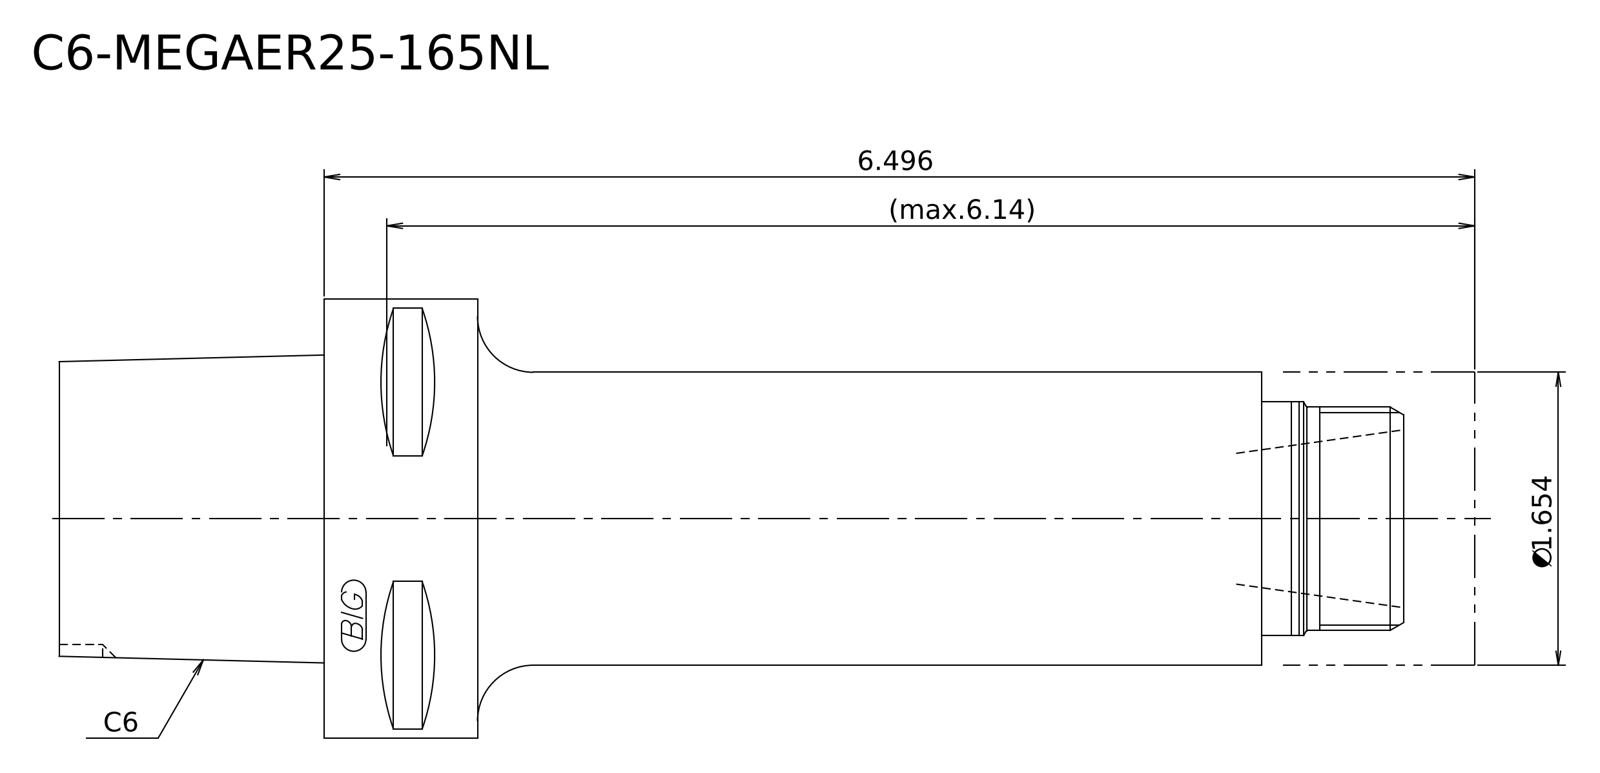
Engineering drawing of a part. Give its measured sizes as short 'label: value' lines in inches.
written by: Kubotek KeyCreator 2011 V10.0.2 (22737) (automotive_design)
unit: in
bodies: 2 solids, 18 faces (7 planar, 5 cylindrical, 6 other)
size: 7.992 × 2.48 × 2.48
volume: 20.67 in³; area: 59.33 in²
bosses: 1× ⌀2.48, 1× ⌀1.654, 1× ⌀1.319, 1× ⌀1.26
face distances: 5.413, 1.083, 6.496, 7.992, 6.909, 1.496, 0.402, 0.681, 6.094, 7.591
